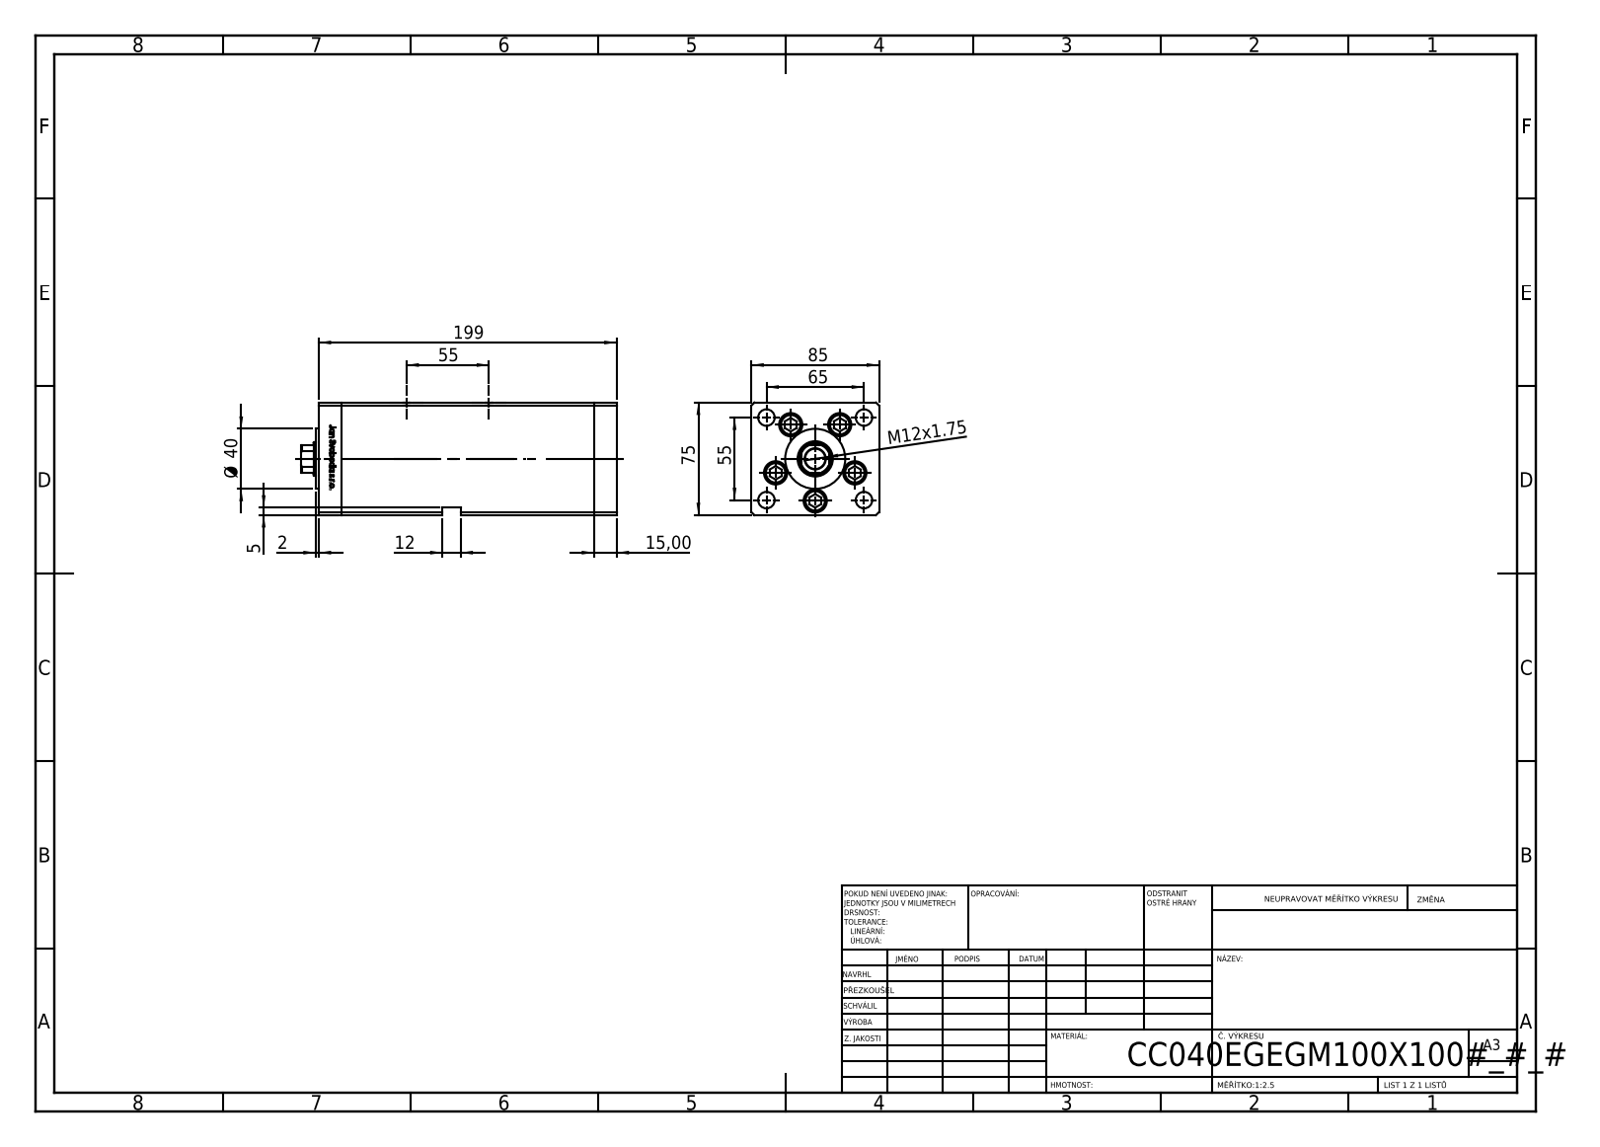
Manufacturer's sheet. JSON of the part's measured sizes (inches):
{"part_name": "V220C_E MIDDLE; V220C_FRONT_E; ALLEN BOLT; V220C BACK_E (+1 more)", "step_written_by": "SolidWorks 2019 (CONFIG_CONTROL_DESIGN)", "units": "inches", "bodies": {"solids": 14, "faces": 1214, "planar": 475, "cylindrical": 165, "other": 574}, "overall_size": [8.268, 3.346, 2.953], "volume_in3": 65.66, "surface_area_in2": 283.4, "round_holes": [[0.433, 9], [0.61, 5], [0.413, 4], [0.65, 4], [0.079, 2], [0.518, 2], [0.531, 1], [0.866, 1], [0.925, 1]], "round_bosses_or_shafts": [[0.571, 5], [0.315, 5], [1.575, 1]], "partial_cylinders_radius": [[0.037, 2], [0.413, 1]], "face_to_face_distances": [3.346, 2.953, 0.591, 6.634, 7.224, 7.815, 1.348, 0.413, 2.539, 2.697], "hole_center_spacings": [1.102, 1.676, 2.165, 2.559, 3.352, 0.664, 0.755, 1.273]}
